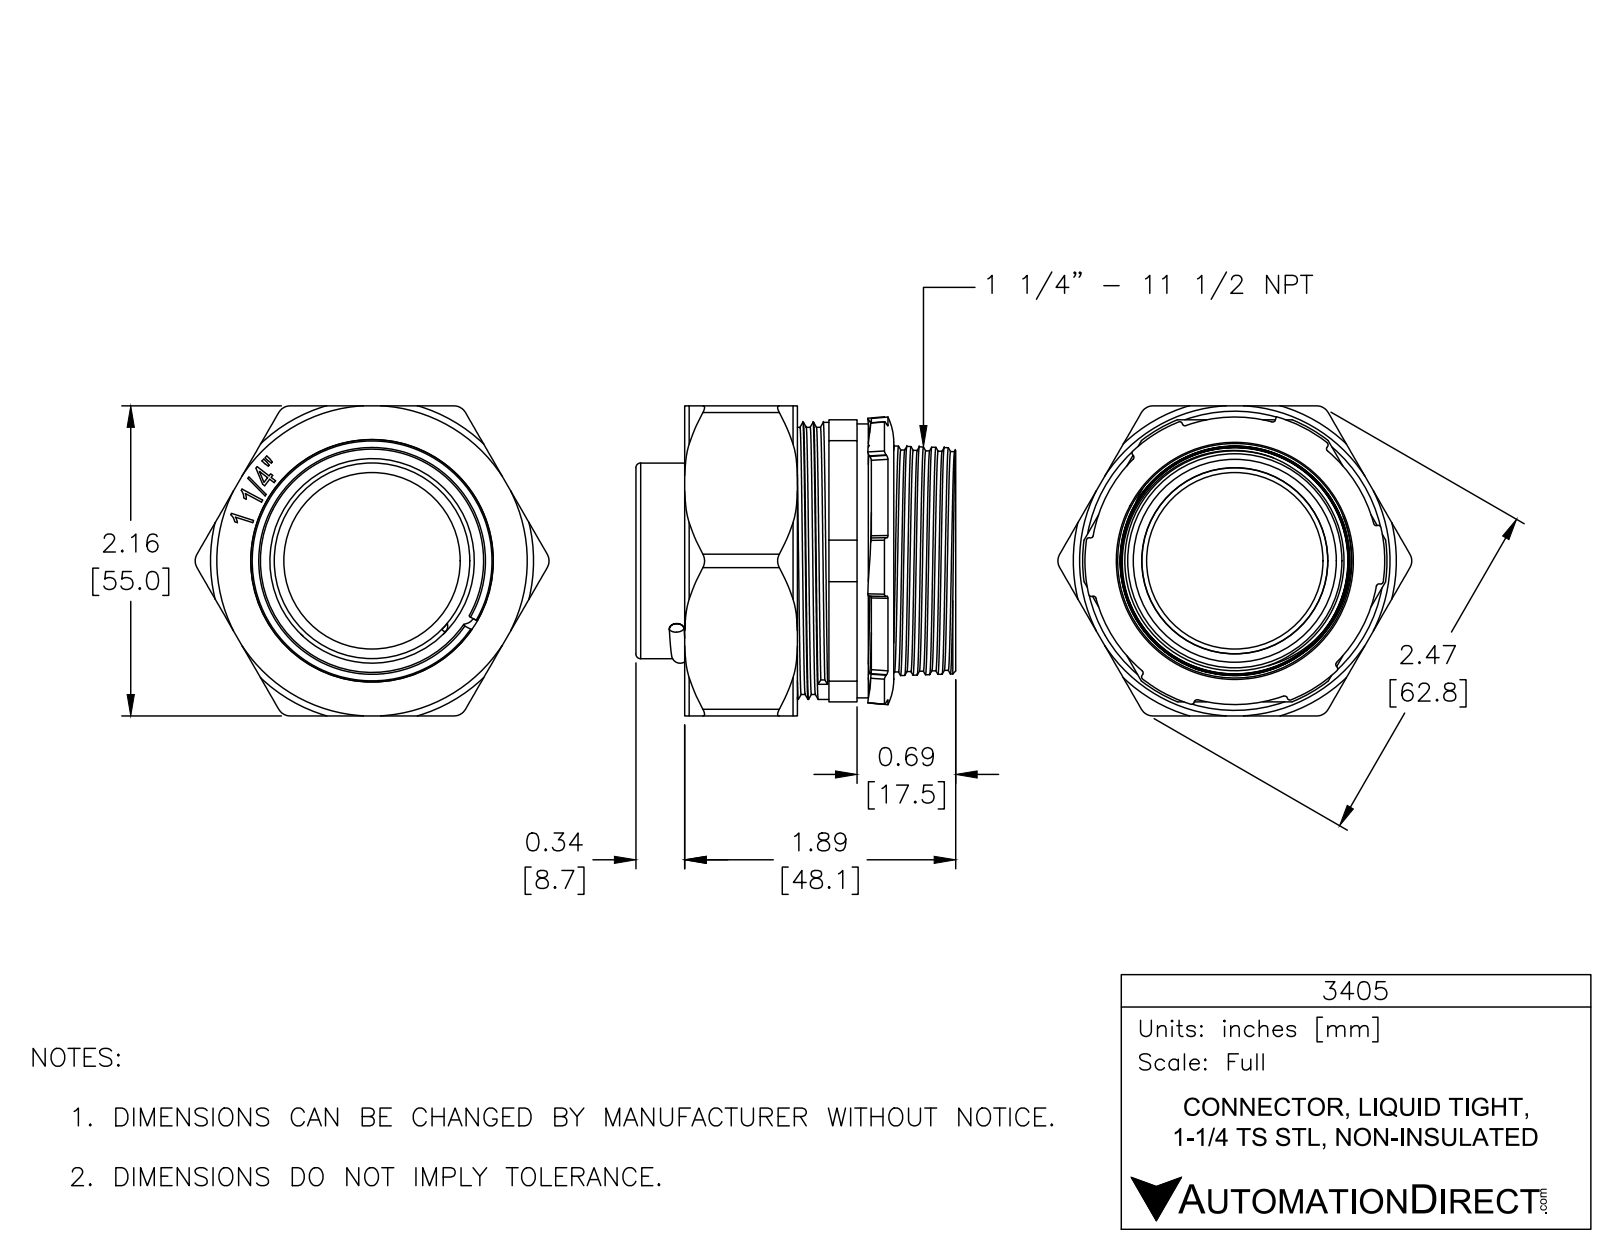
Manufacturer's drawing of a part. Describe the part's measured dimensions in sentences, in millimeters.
The part is named "3405". Its 3-D file was written by "SolidWorks 2018 (AUTOMOTIVE_DESIGN)". It is 6 solids with 524 faces: 212 planar, 122 cylindrical and 190 other. Overall it measures 62.8 by 56.7 by 55 millimeters. Its volume is 39 180 cubic millimeters and its surface area 41 320 square millimeters. Round holes: 1 of diameter 4.6, 1 of diameter 31.3, 1 of diameter 33, 1 of diameter 36, 1 of diameter 39.5, 1 of diameter 41.6, 1 of diameter 42.3, 1 of diameter 43, 1 of diameter 44.7, 1 of diameter 48.5. Round bosses or shafts: 1 of diameter 49.1, 1 of diameter 48.6, 1 of diameter 47.5, 1 of diameter 47.4, 1 of diameter 44, 1 of diameter 34.7, 1 of diameter 33, 1 of diameter 3.8. Partial cylindrical surfaces (rounded edges, fillets, slot ends): 8 of radius 0.3, 6 of radius 2.4, 2 of radius 0.1, 2 of radius 1.3, 1 of radius 0.2, 1 of radius 0.4, 1 of radius 0.6, 1 of radius 27. The main face-to-face distances are 55, 30.6, 2.5, 52.5, 32.6, 2, 23.6, 7, 9, 10.6. The hole center spacings are 24.5.
